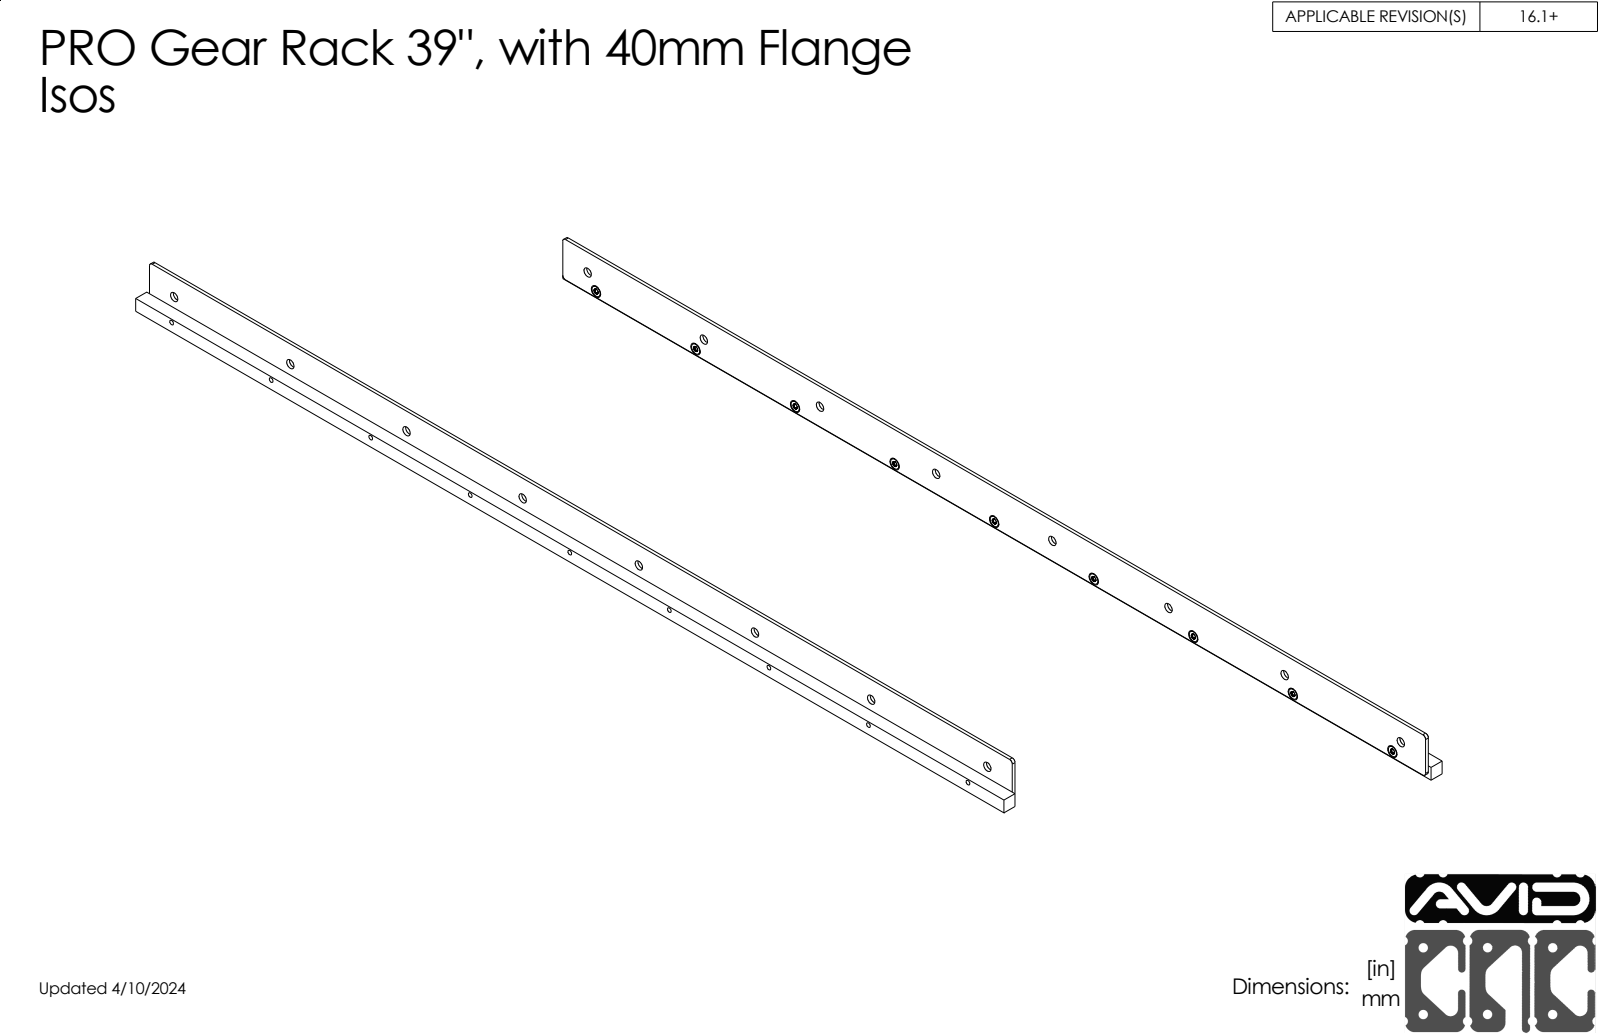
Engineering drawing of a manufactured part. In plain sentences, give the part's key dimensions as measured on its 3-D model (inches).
The part is named "MGM-XX-BAR-40_39\" Bar; Flathead Machine Screws, Torx Drive - Metric_FH-M5-10-TX; MG-XX-ME-PRO_39\"; MGM-39-40_16.1". Its 3-D file was written by "SolidWorks 2020 (CONFIG_CONTROL_DESIGN)". It is 11 solids with 365 faces: 30 planar, 92 cylindrical and 243 other. Overall it measures 39.25 by 1.715 by 0.625 inches. Its volume is 17.37 cubic inches and its surface area 217.5 square inches. Round holes: 9 of diameter 0.165, 9 of diameter 0.217, 8 of diameter 0.33. Round bosses or shafts: 9 of diameter 0.366, 9 of diameter 0.197. Partial cylindrical surfaces (rounded edges, fillets, slot ends): 4 of radius 0.125. The main face-to-face distances are 0.125, 0.5, 0.625, 0.14, 1.715, 0.36, 1.575, 1.215, 0.121, 0.621. The hole center spacings are 4.5, 5.251, 9, 10.502, 13.5, 15.754, 18, 21.005.
